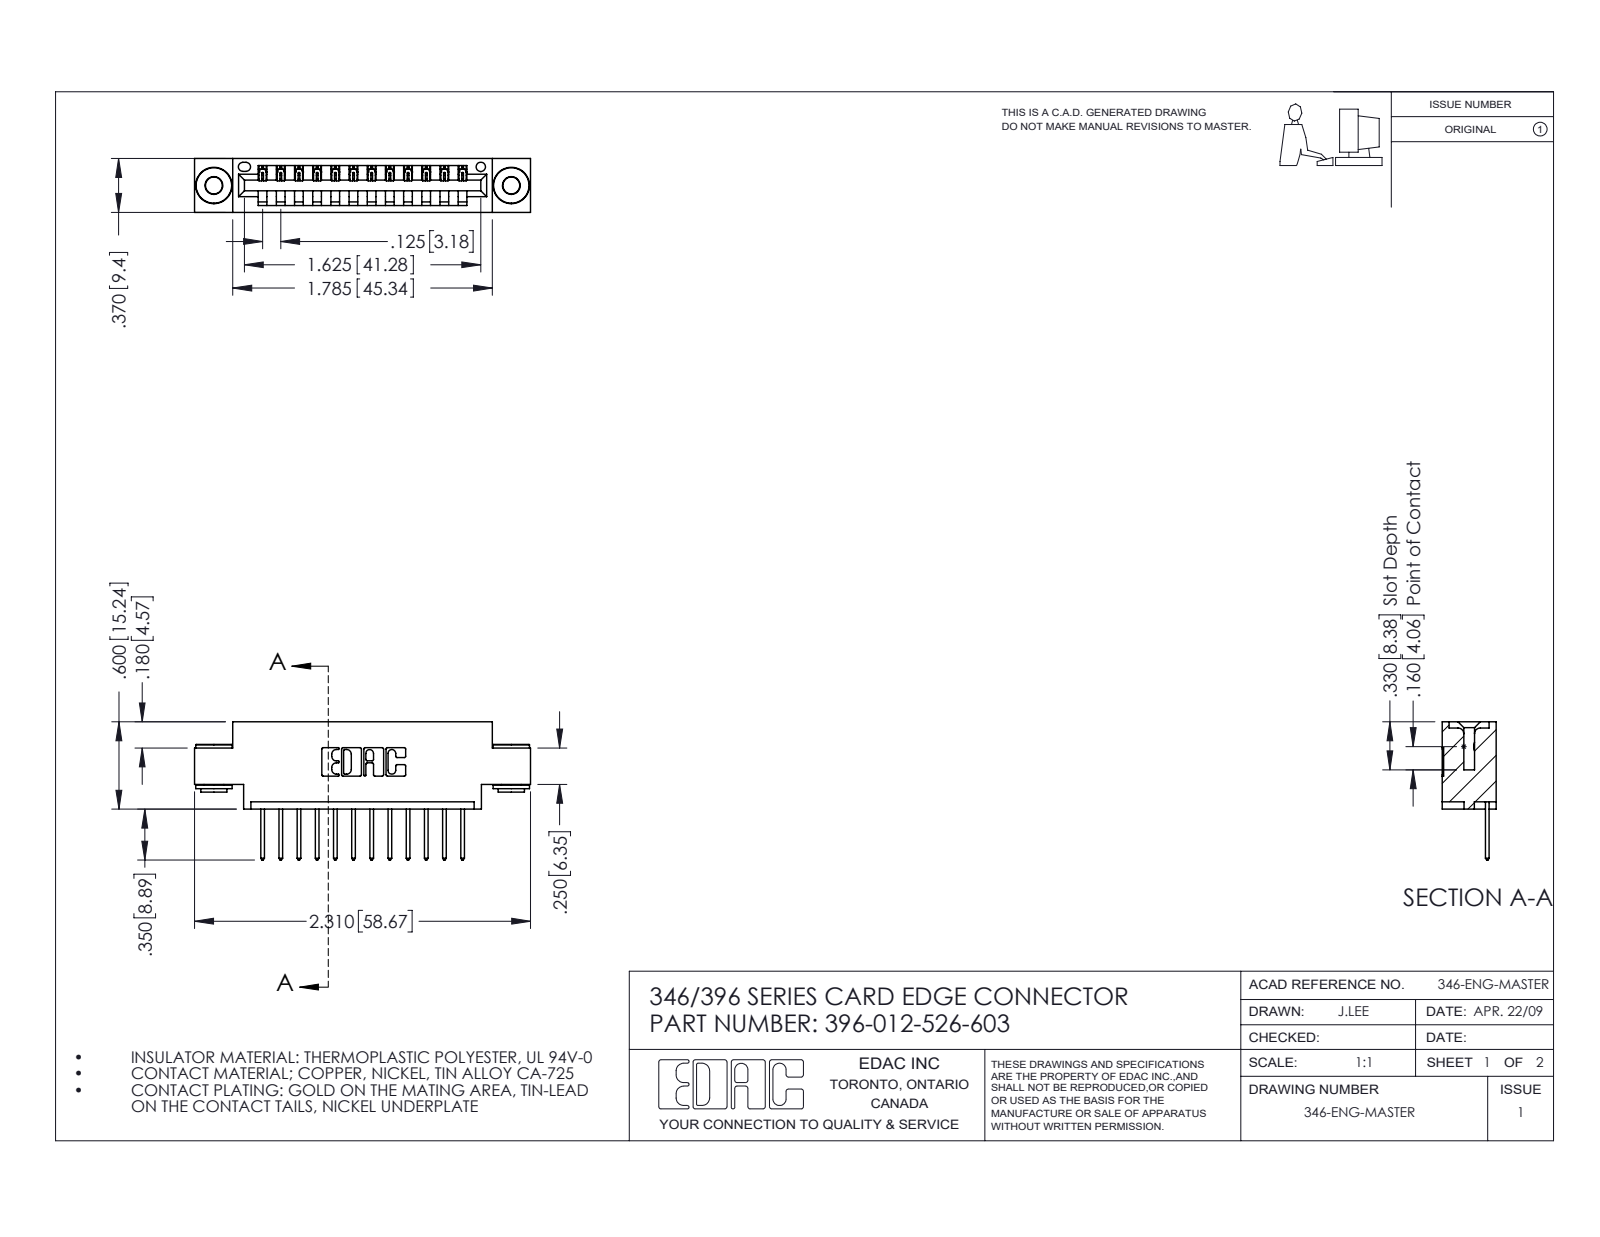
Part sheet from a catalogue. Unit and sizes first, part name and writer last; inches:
Units: inches
Overall size (bounding box): 2.31 × 0.95 × 0.37
Round holes (diameter × count): ⌀0.116 ×2, ⌀0.156 ×2, ⌀0.064 ×1
Round bosses / shafts (diameter × count): ⌀0.25 ×2, ⌀0.18 ×2, ⌀0.136 ×2
Partial cylindrical surfaces — rounded edges, fillets, slot ends (radius × count): R0.006 ×24, R0.01 ×24, R0.01 ×22, R0.007 ×6, R0.031 ×6, R0.026 ×3, R0.031 ×2, R0.04 ×2
Main face-to-face distances: 0.25, 0.37, 0.048, 0.322, 0.025, 0.072, 0.298, 0.148, 0.222, 0.1
Hole centre spacings: 0.246, 1.839, 2.045
Volume: 0.321 in³ · Surface area: 10.27 in²
Bodies: 15 solids, 860 faces (570 planar, 282 cylindrical, 8 other)
Part name (STEP PRODUCT): 345-250-002_345-250-002-102; 345-292-001_345-293-126; 346 Part_0.170 Offset - 0.156 Dia-TH; 396-012-526-603
STEP written by: SolidWorks 2016 (CONFIG_CONTROL_DESIGN)
